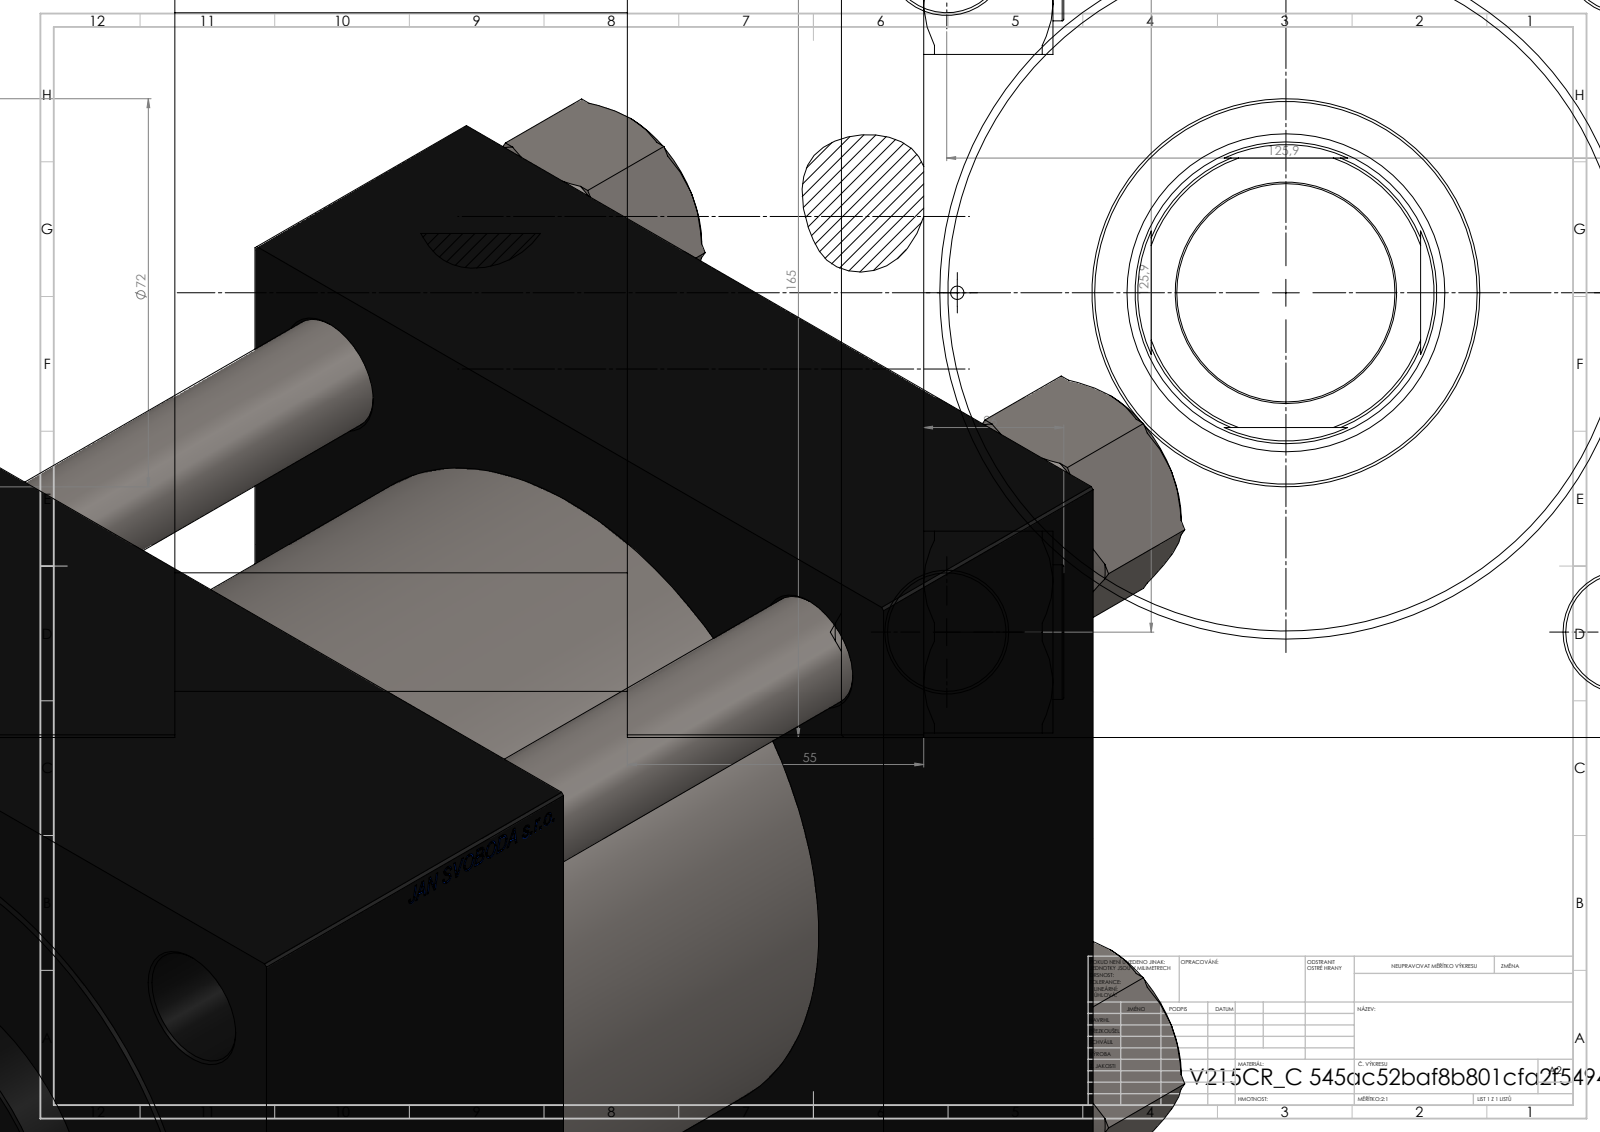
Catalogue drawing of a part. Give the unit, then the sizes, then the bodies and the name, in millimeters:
Units: millimetres
Overall size (bounding box): 278 × 169.14 × 165
Round holes (diameter × count): ⌀22 ×4, ⌀2.5 ×2, ⌀7 ×2, ⌀32.24 ×2, ⌀45 ×2, ⌀40.5 ×1, ⌀56 ×1, ⌀59 ×1, ⌀96 ×1, ⌀125 ×1, ⌀125.5 ×1
Round bosses / shafts (diameter × count): ⌀25 ×4, ⌀131 ×1, ⌀72 ×1
Partial cylindrical surfaces — rounded edges, fillets, slot ends (radius × count): R27 ×1
Main face-to-face distances: 165, 55, 162, 217, 139, 84, 78, 188.3, 133.3, 49.3
Hole centre spacings: 62.98, 89.02, 125.9, 139.02, 61, 178.05, 122, 138.5
Volume: 4 494 000 mm³ · Surface area: 503 848 mm²
Bodies: 11 solids, 1202 faces (576 planar, 90 cylindrical, 536 other)
Part name (STEP PRODUCT): V215CR_C_Body; NUT_M5_C; V215_VC_A; V215CR_VCP_C (+1 more)
STEP written by: SolidWorks 2019 (CONFIG_CONTROL_DESIGN)
